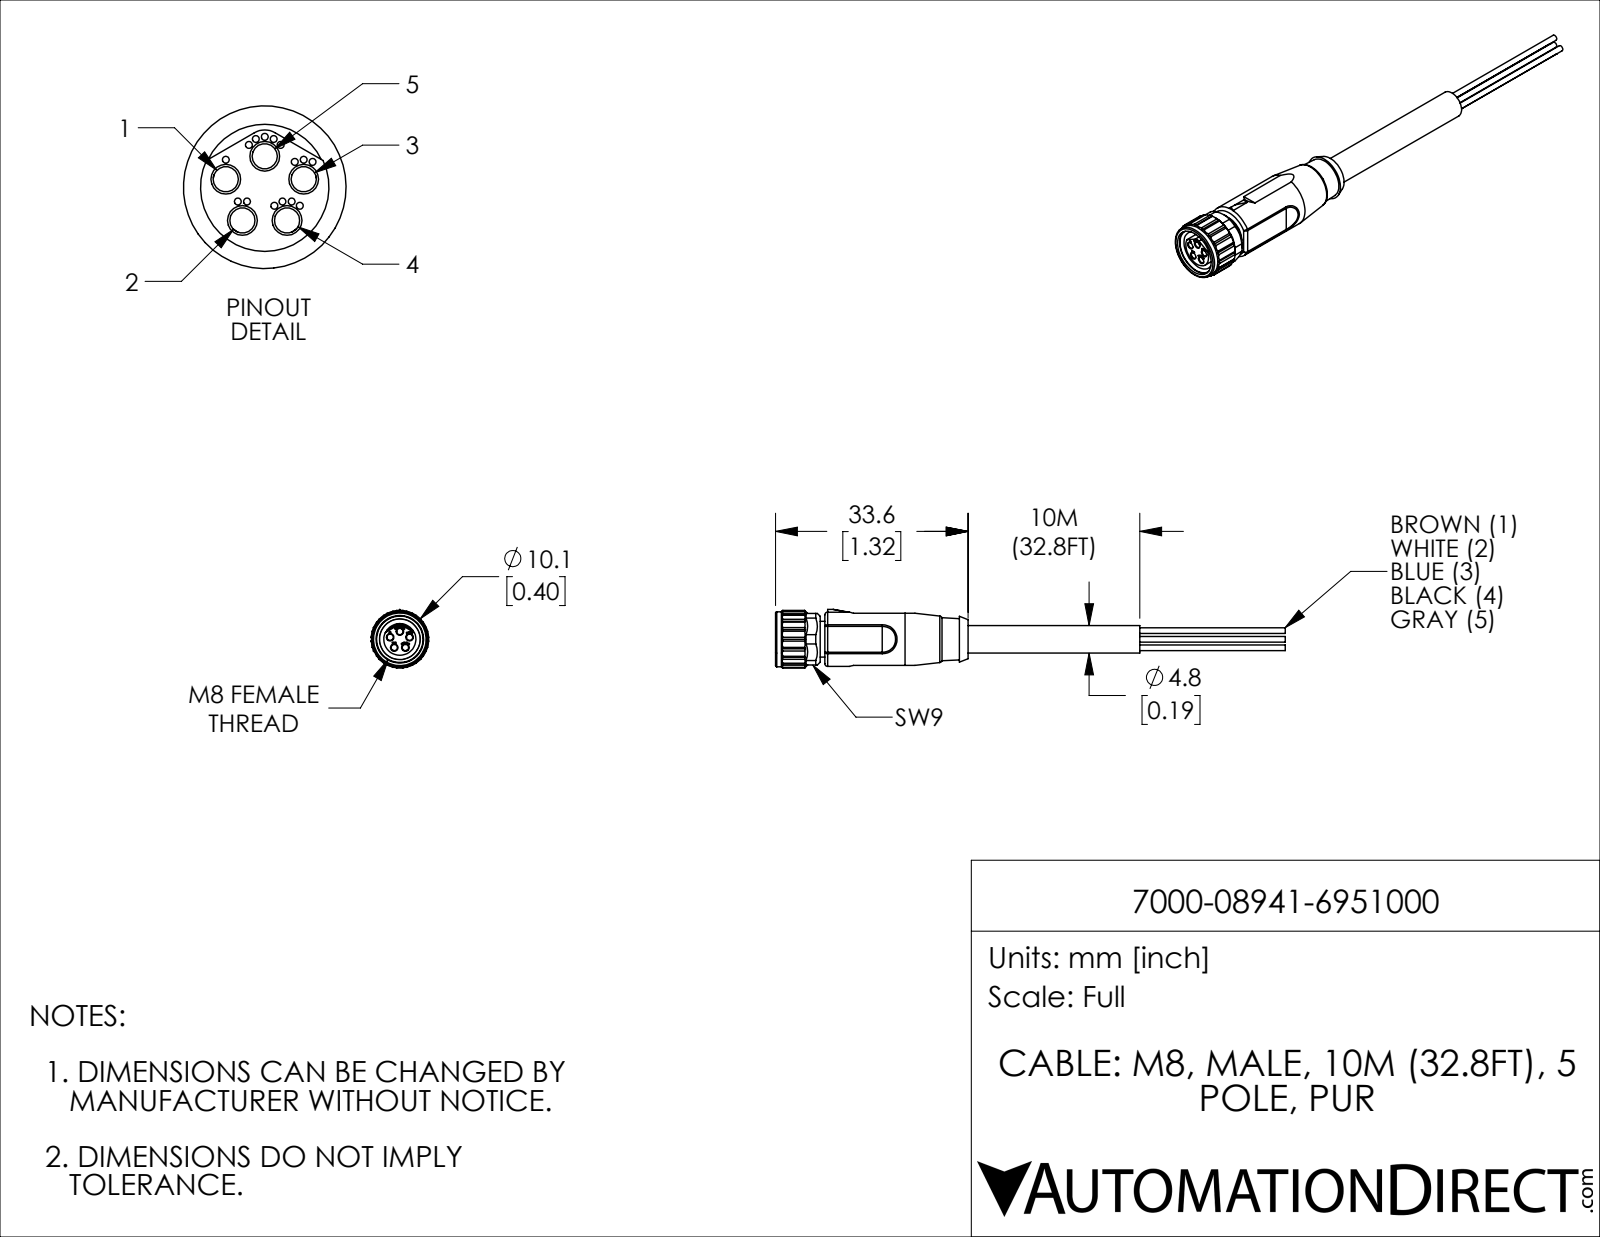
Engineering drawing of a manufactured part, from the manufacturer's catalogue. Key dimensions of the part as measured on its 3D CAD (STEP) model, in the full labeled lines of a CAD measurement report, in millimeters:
Part name (STEP PRODUCT): 7000-08941-6951000
STEP written by: SolidWorks 2019 (CONFIG_CONTROL_DESIGN)
Units: millimetres
Bodies: 1 solid, 285 faces (111 planar, 127 cylindrical, 47 other)
Overall size (bounding box): 89 × 10.2 × 10.1
Volume: 2 620 mm³ · Surface area: 2 297 mm²
Round holes (diameter × count): ⌀0.3 ×15, ⌀1.1 ×5, ⌀6.1 ×1, ⌀7.1 ×1, ⌀8.3 ×1
Round bosses / shafts (diameter × count): ⌀1 ×5, ⌀9.6 ×1, ⌀9.5 ×1, ⌀6.2 ×1, ⌀4.8 ×1
Partial cylindrical surfaces — rounded edges, fillets, slot ends (radius × count): R2 ×18, R0.5 ×6, R0.8 ×6, R0.8 ×4, R0.2 ×2, R5 ×2, R0.9 ×1, R2.3 ×1
Main face-to-face distances: 8.2, 9.1, 9.1, 0.8, 25.8, 25, 9, 7.1, 7.9, 32.9
Hole centre spacings: 0.8, 0.4, 2, 0.8, 1.1, 1.8, 2, 2.5
